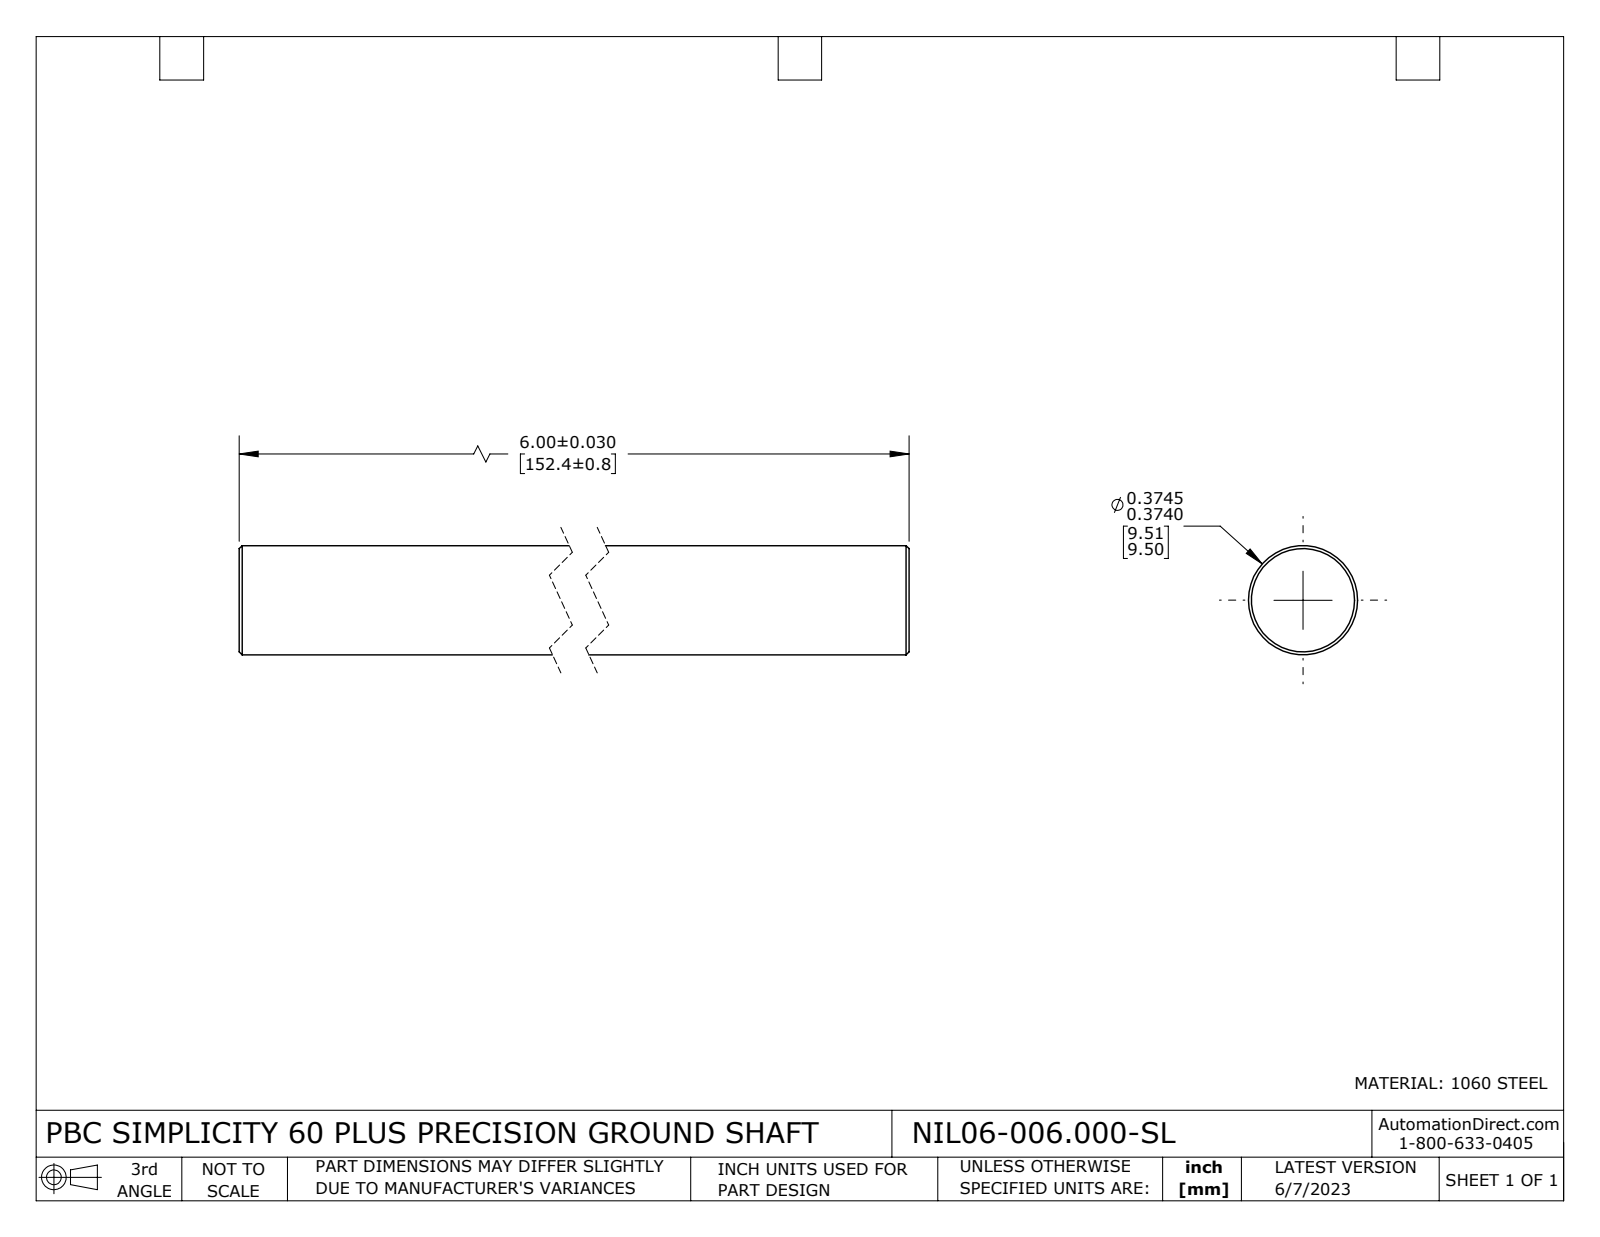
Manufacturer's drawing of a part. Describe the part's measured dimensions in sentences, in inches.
The part is named "NIL06-006.000-SL". Its 3-D file was written by "SolidWorks 2021 (CONFIG_CONTROL_DESIGN)". It is 1 solid with 8 faces: 2 planar, 2 cylindrical and 4 other. Overall it measures 6 by 0.375 by 0.375 inches. Its volume is 0.663 cubic inches and its surface area 7.275 square inches. Round bosses or shafts: 1 of diameter 0.375. The main face-to-face distances are 6.
